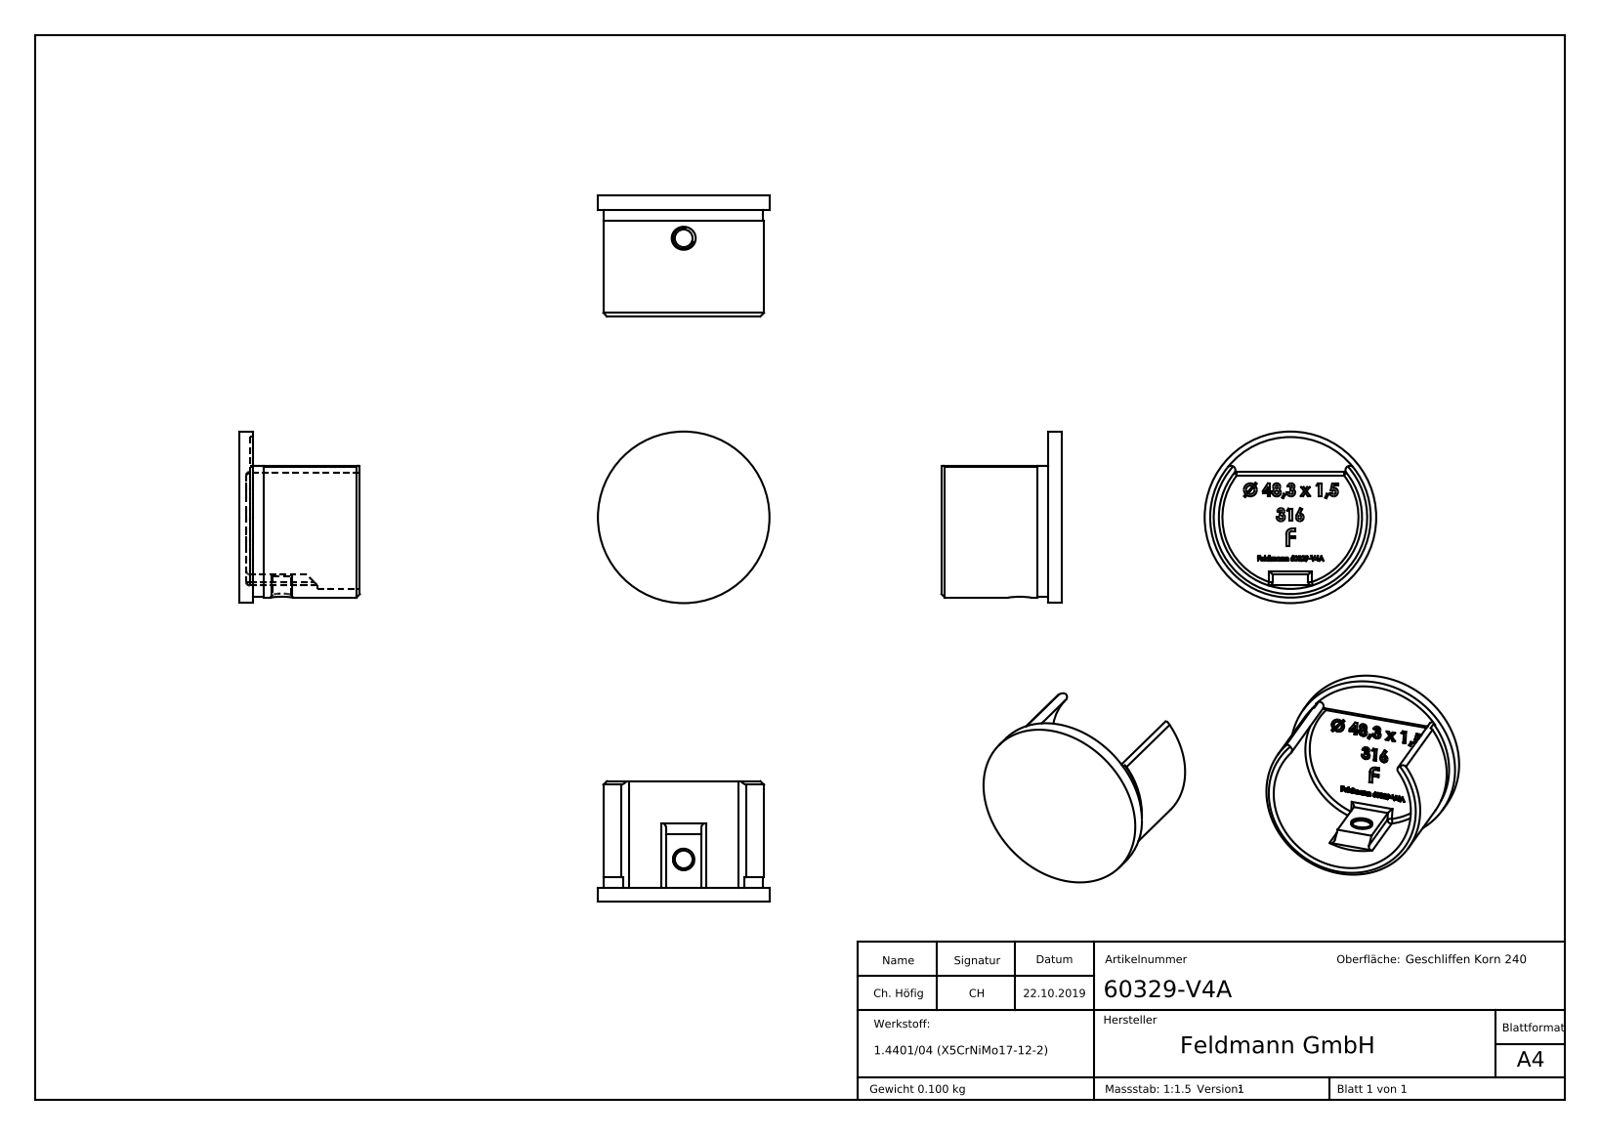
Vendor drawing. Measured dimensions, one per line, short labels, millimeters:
name: 60329-V4A
written by: SolidWorks 2015 (CONFIG_CONTROL_DESIGN)
unit: mm
bodies: 1 solid, 429 faces (239 planar, 14 cylindrical, 176 other)
size: 48.3 × 48.3 × 34
volume: 12 365 mm³; area: 10 564 mm²
holes: 1× ⌀5, 1× ⌀45.2
bosses: 1× ⌀48.3
rounds: 6× R1, 2× R1.23, 1× R20.15, 1× R22.4
face distances: 2, 1, 4, 3, 30, 31, 32, 34, 1.9, 2.1
